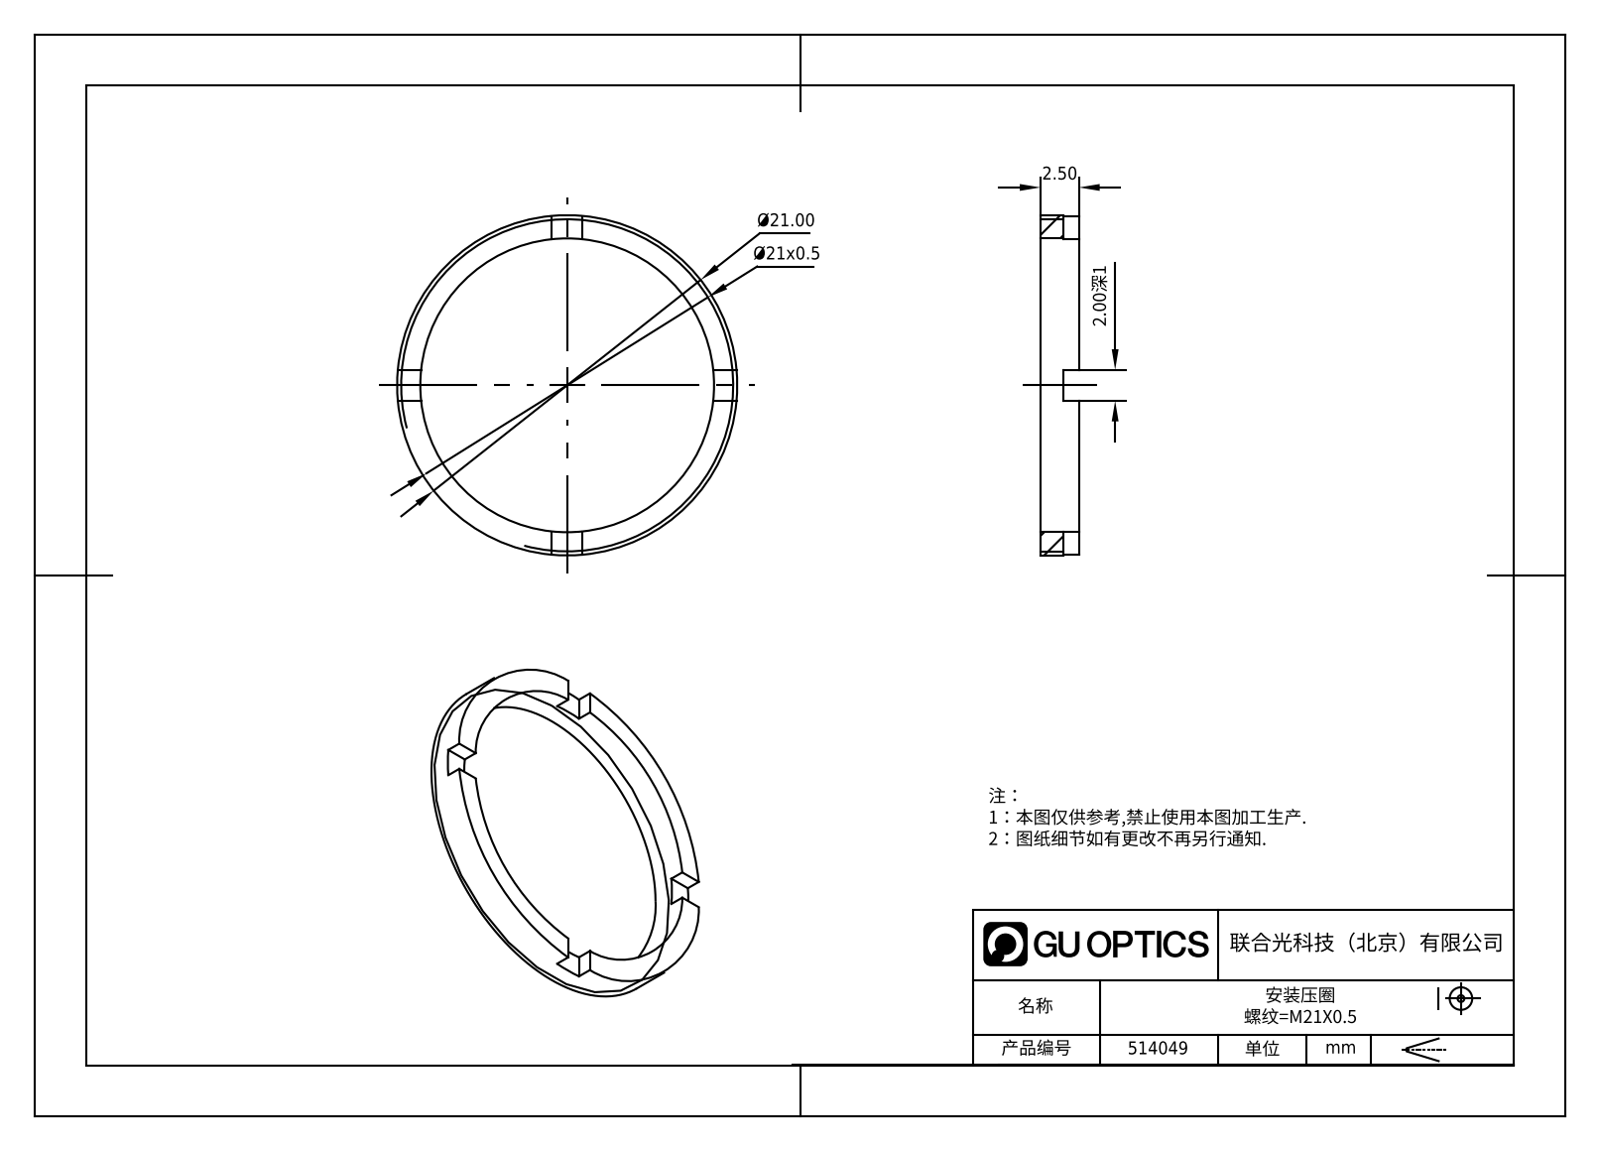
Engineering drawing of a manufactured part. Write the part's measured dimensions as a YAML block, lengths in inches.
part_name: "514049"
step_written_by: "SolidWorks 2020 (CONFIG_CONTROL_DESIGN)"
units: inches
bodies: {solids: 1, faces: 21, planar: 17, cylindrical: 4, other: 0}
overall_size: [0.827, 0.827, 0.098]
volume: 0.013
surface_area: 0.753
round_holes:
  - {diameter: 0.709, count: 1}
round_bosses_or_shafts:
  - {diameter: 0.827, count: 1}
face_to_face_distances: [0.098, 0.059, 0.039, 0.079]
